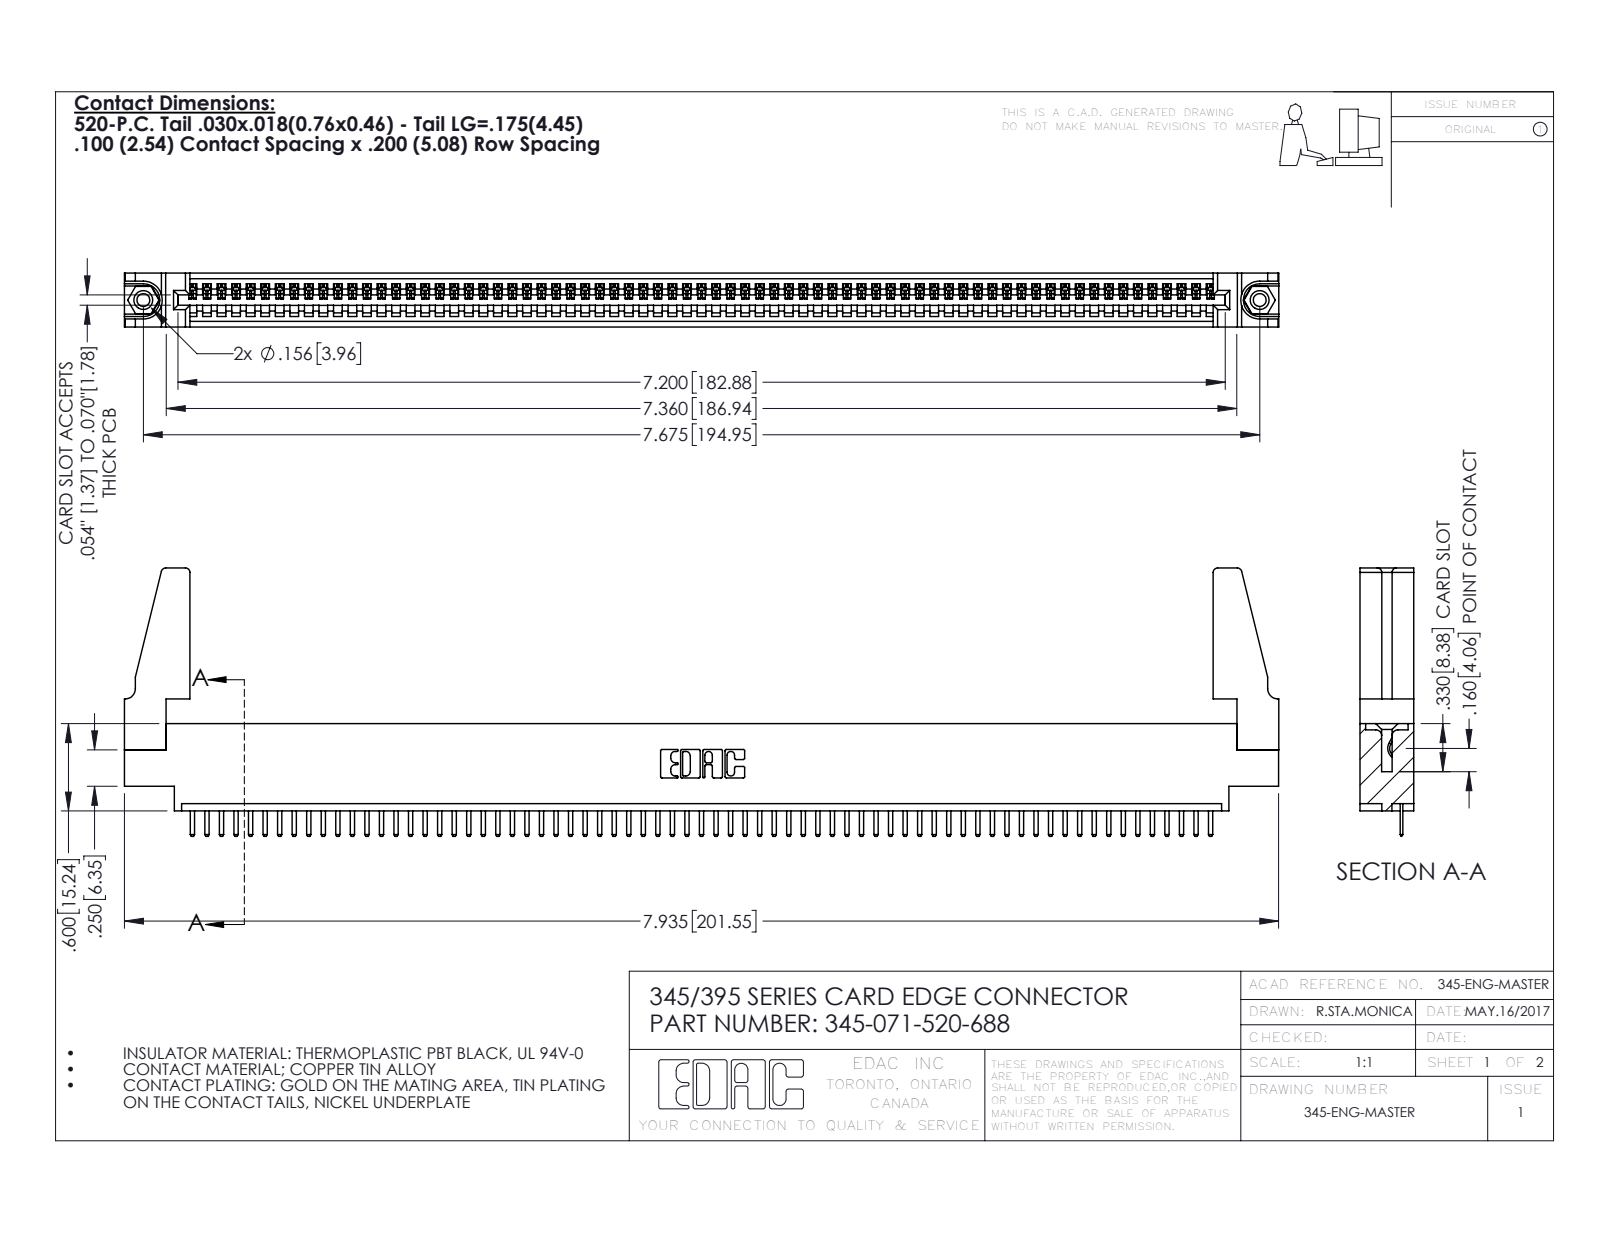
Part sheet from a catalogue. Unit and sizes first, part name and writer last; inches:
Units: inches
Overall size (bounding box): 7.936 × 1.845 × 0.37
Round holes (diameter × count): ⌀0.089 ×2, ⌀0.125 ×2, ⌀0.156 ×2, ⌀0.064 ×1
Round bosses / shafts (diameter × count): ⌀0.155 ×2
Partial cylindrical surfaces — rounded edges, fillets, slot ends (radius × count): R0.01 ×144, R0.006 ×142, R0.01 ×22, R0.03 ×8, R0.007 ×6, R0.031 ×6, R0.026 ×3, R0.031 ×2
Main face-to-face distances: 0.072, 0.298, 0.37, 0.098, 0.272, 0.025, 0.2, 0.225, 0.072, 0.175
Hole centre spacings: 0.27, 7.439, 7.675
Volume: 1.362 in³ · Surface area: 43.89 in²
Bodies: 76 solids, 4656 faces (3138 planar, 1502 cylindrical, 16 other)
Part name (STEP PRODUCT): 345 Part_0.170 Offset - 0.156 Dia-TH; 345-250-001_345-250-001-102; 345-220-078_345-220-088; 345-071-520-688 (+1 more)
STEP written by: SolidWorks 2016 (CONFIG_CONTROL_DESIGN)
